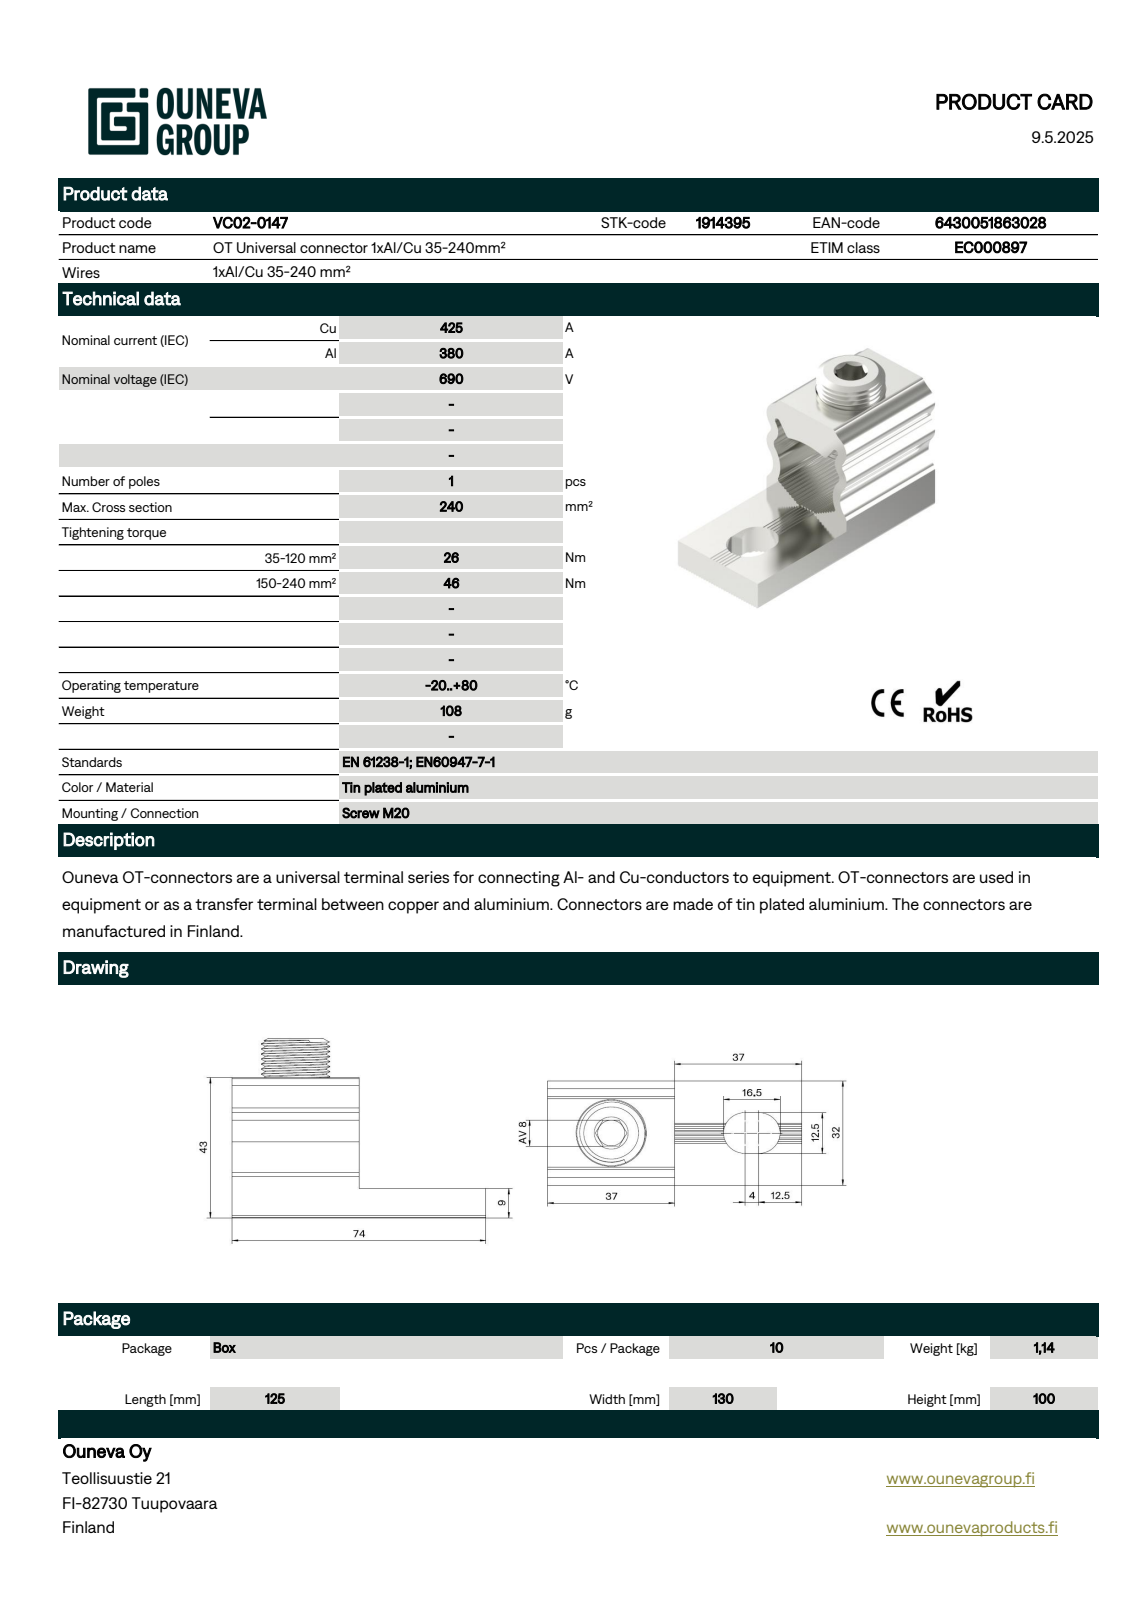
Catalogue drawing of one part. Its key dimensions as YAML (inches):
part_name: "Liitinrunko_OT_1x240"
step_written_by: "Creo Elements/Direct Modeling 20.6A 14-Oct-2023 (C) Parametric Technology GmbH (AUTOMOTIVE_DESIGN)"
units: inches
bodies: {solids: 1, faces: 313, planar: 130, cylindrical: 177, other: 6}
overall_size: [2.913, 2.165, 1.26]
volume: 2.603
surface_area: 24.58
round_bosses_or_shafts:
  - {diameter: 0.787, count: 1}
partial_cylinders:
  - {radius: 0.01, count: 63}
  - {radius: 0.012, count: 41}
  - {radius: 0.039, count: 10}
  - {radius: 0.079, count: 6}
  - {radius: 0.094, count: 2}
  - {radius: 0.189, count: 2}
  - {radius: 0.193, count: 2}
  - {radius: 0.197, count: 2}
face_to_face_distances: [1.457, 1.26, 1.339, 0.057, 0.472, 0.114, 0.028, 0.085, 0.143, 2.913]
